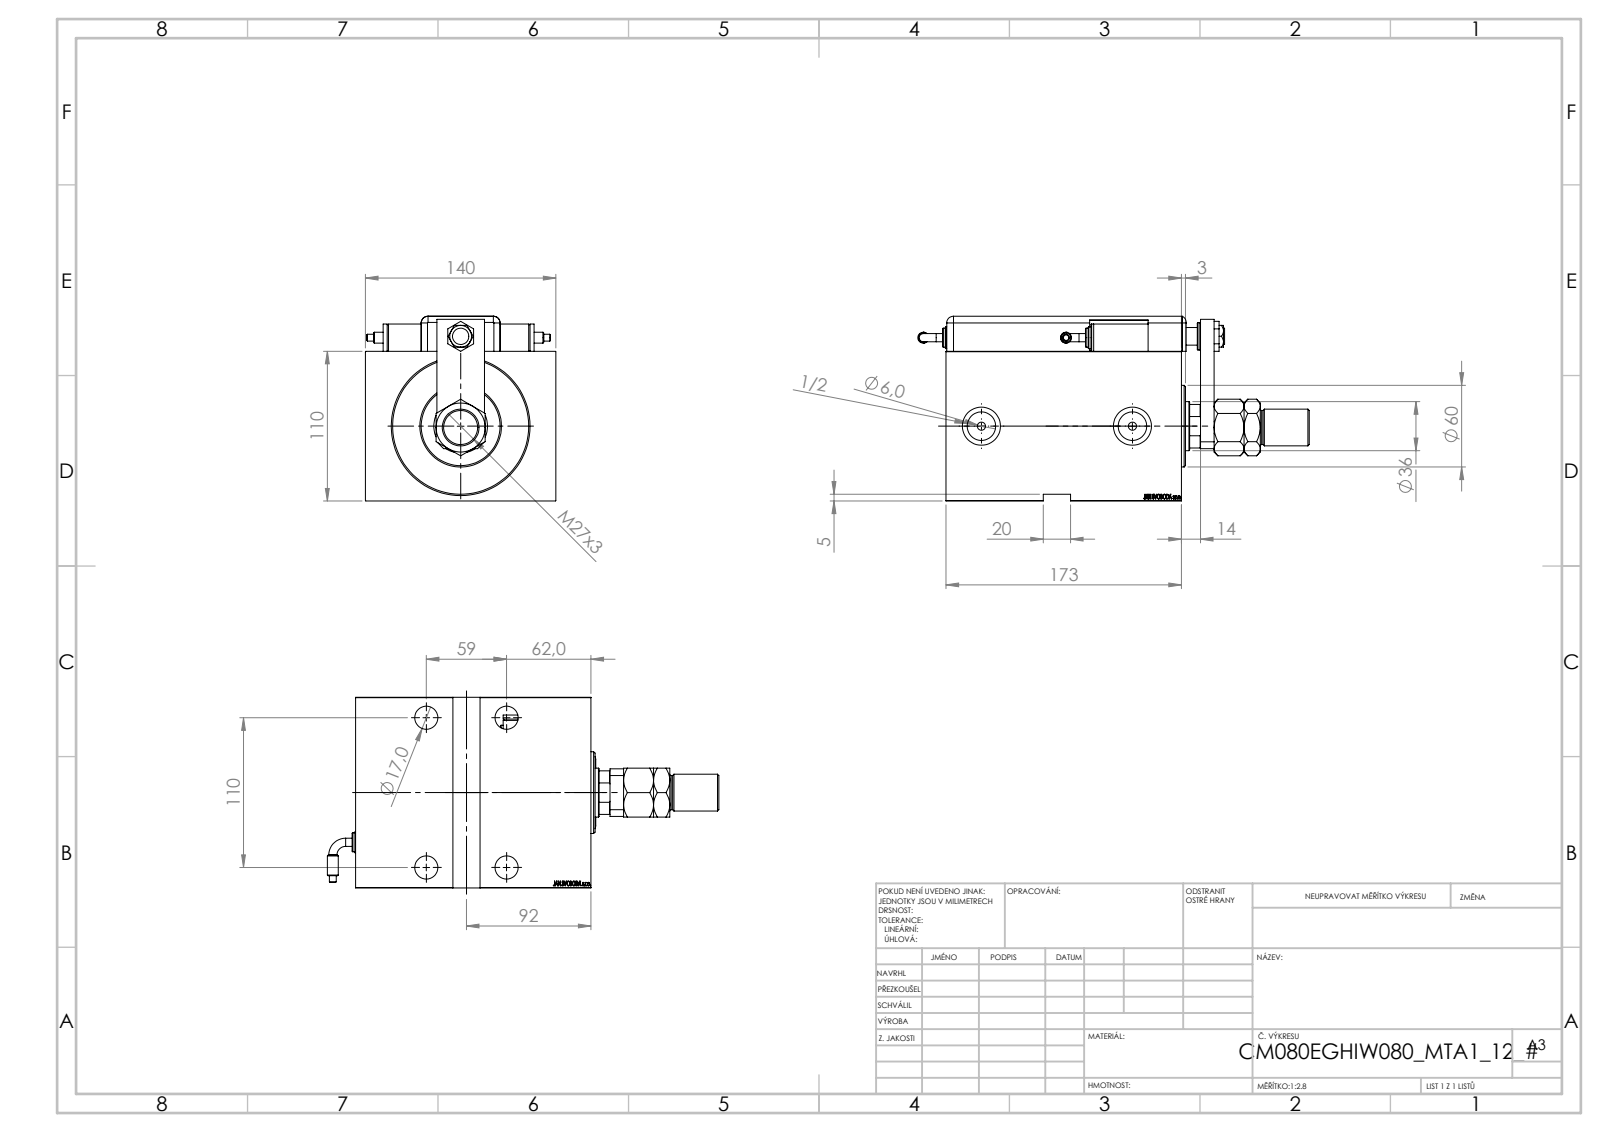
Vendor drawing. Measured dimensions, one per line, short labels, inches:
name: SWITCH_Q_FRONT_BACK; SWITCH Q; V450CM_E_VCP; SWITCH DIM A_G (+7 more)
written by: SolidWorks 2019 (CONFIG_CONTROL_DESIGN)
unit: in
bodies: 14 solids, 1320 faces (636 planar, 121 cylindrical, 563 other)
size: 11.329 × 5.512 × 5.346
volume: 143.5 in³; area: 506.3 in²
holes: 4× ⌀0.669, 4× ⌀0.984, 2× ⌀0.157, 2× ⌀0.236, 2× ⌀0.315, 2× ⌀0.825, 2× ⌀1.102, 1× ⌀0.472, 1× ⌀0.512, 1× ⌀0.551, 1× ⌀1.004, 1× ⌀1.063
bosses: 3× ⌀0.787, 2× ⌀0.63, 2× ⌀0.551, 2× ⌀0.315, 2× ⌀0.236, 2× ⌀0.198, 1× ⌀2.362, 1× ⌀0.984
rounds: 9× R0.197, 1× R0.394, 1× R0.689
face distances: 4.331, 5.512, 0.118, 6.811, 0.827, 5.984, 0.197, 5.346, 1.016, 1.614
hole spacings: 2.323, 2.798, 3.352, 4.331, 4.825, 4.914, 5.167, 0.039
